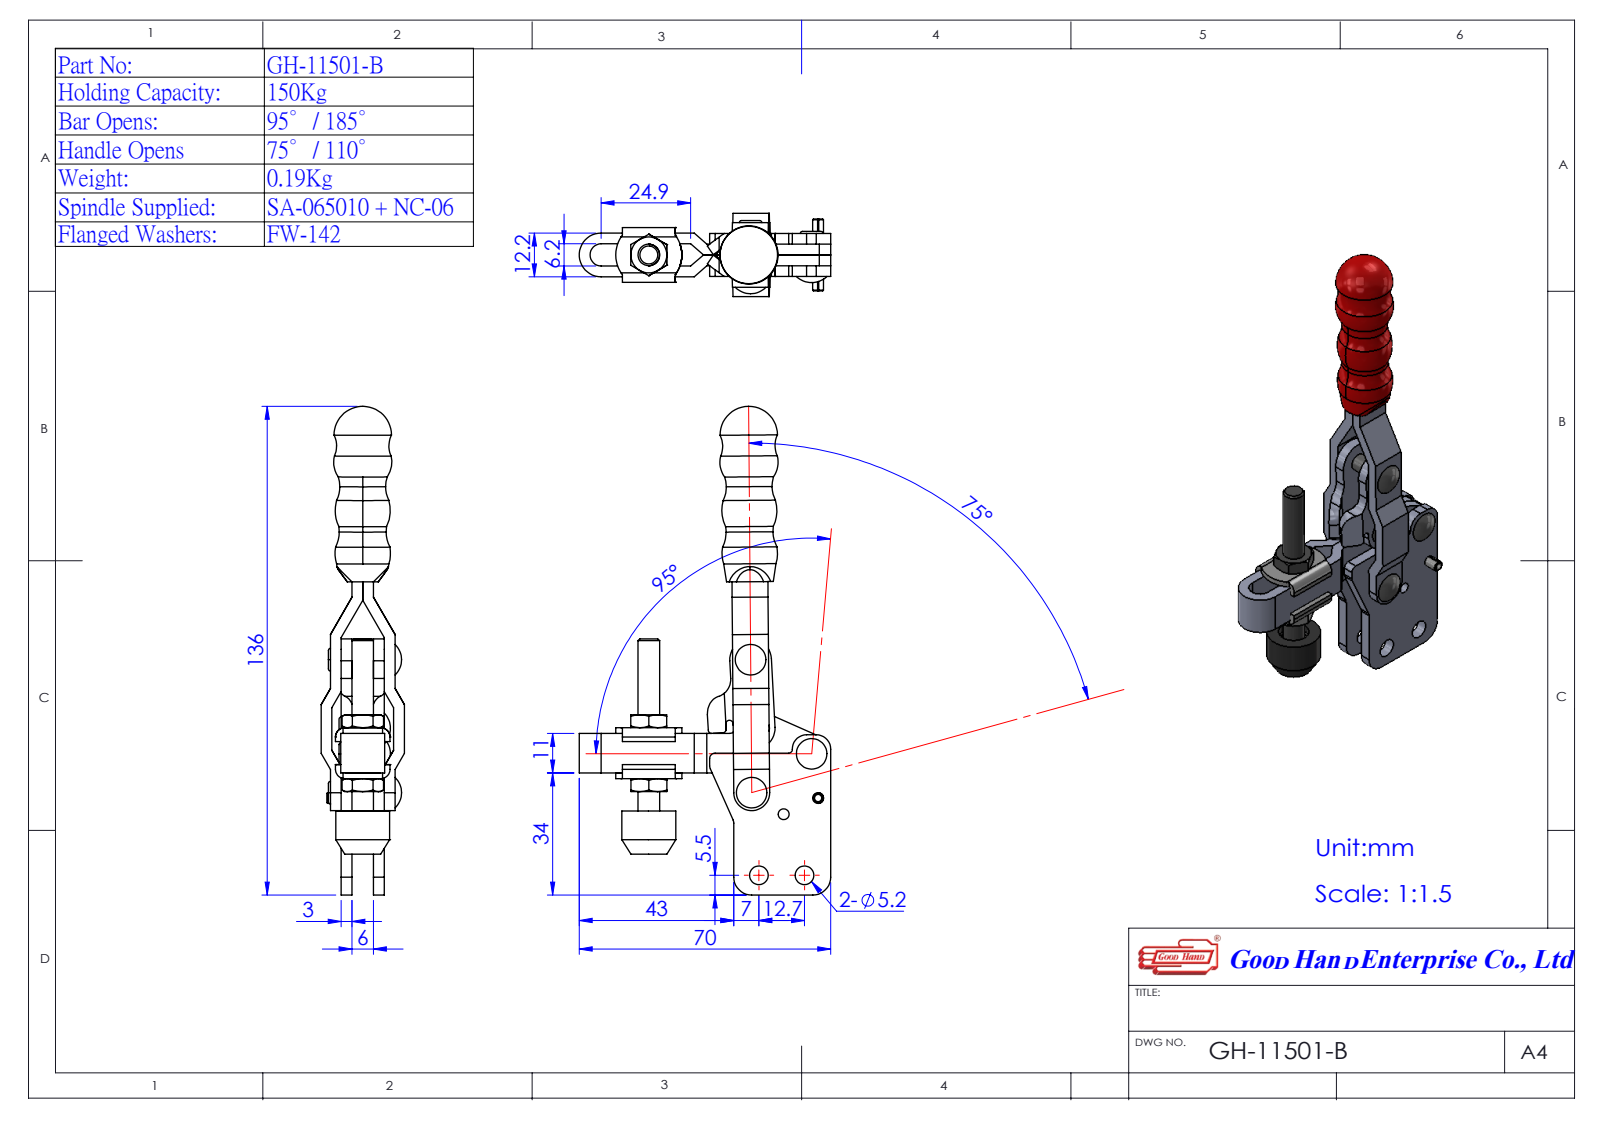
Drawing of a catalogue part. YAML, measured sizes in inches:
part_name: "111502B08-1^GH-11501-B(簡化)-1; GH-11501-B(簡化)-1; Group1^GH-11501-B(簡化)-1; Group4^GH-11501-B(簡化)-1 (+2 more)"
step_written_by: "SolidWorks 2016 (AUTOMOTIVE_DESIGN)"
units: inches
bodies: {solids: 9, faces: 312, planar: 142, cylindrical: 104, other: 66}
overall_size: [5.355, 2.756, 0.965]
volume: 1.899
surface_area: 34.1
round_holes:
  - {diameter: 0.118, count: 6}
  - {diameter: 0.209, count: 2}
round_bosses_or_shafts:
  - {diameter: 0.191, count: 2}
  - {diameter: 0.591, count: 1}
  - {diameter: 0.236, count: 1}
partial_cylinders:
  - {radius: 0.039, count: 9}
  - {radius: 0.102, count: 4}
  - {radius: 0.197, count: 4}
  - {radius: 0.079, count: 2}
  - {radius: 0.157, count: 2}
  - {radius: 0.209, count: 2}
  - {radius: 0.228, count: 2}
  - {radius: 0.059, count: 1}
face_to_face_distances: [0.118, 0.236, 0.354, 0.472, 0.122, 0.24, 0.358, 0.476, 0.114, 0.217]
hole_center_spacings: [0.414, 0.422, 0.497, 0.5, 0.689, 0.705, 0.707, 0.722]
